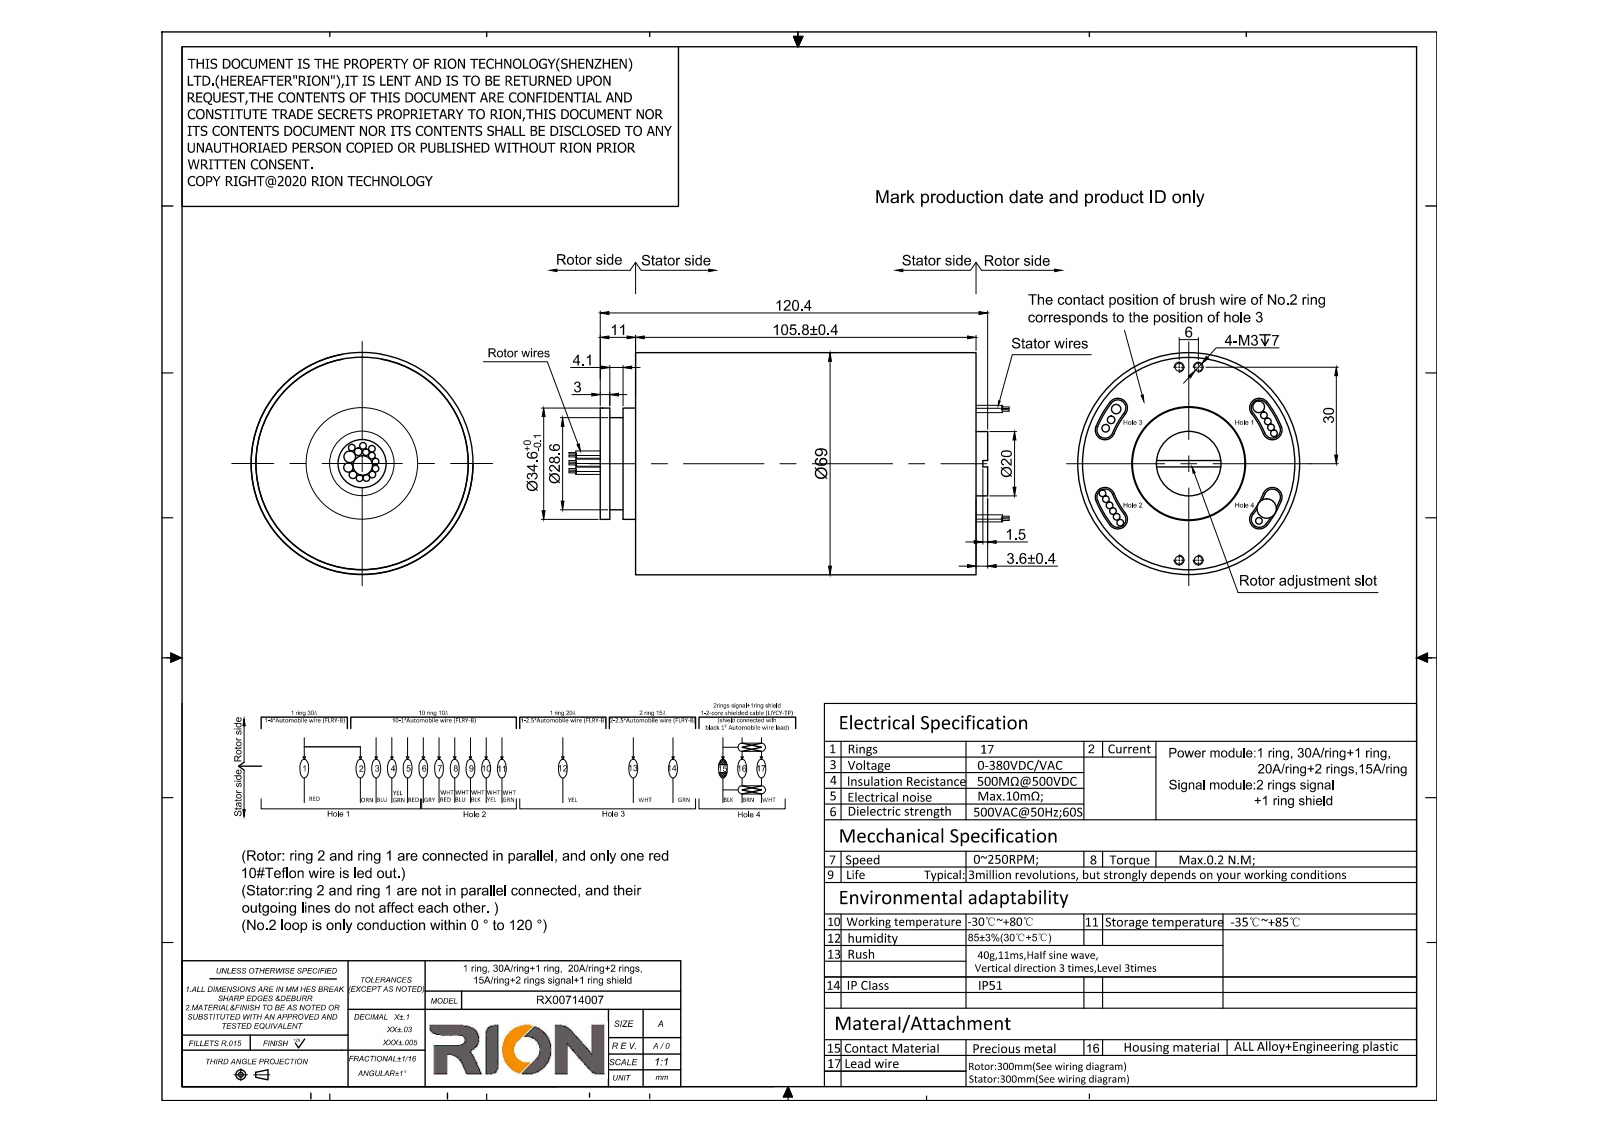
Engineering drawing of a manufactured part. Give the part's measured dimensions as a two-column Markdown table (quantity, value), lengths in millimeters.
| quantity | value |
| --- | --- |
| part name | RZ086-P0130-P0120-P0215-P1010-S03 |
| STEP written by | SolidWorks 2014 (CONFIG_CONTROL_DESIGN) |
| units | millimeters |
| bodies | 1 solid, 154 faces (45 planar, 101 cylindrical, 8 other) |
| overall size | 158.3 × 69 × 69 |
| volume | 408 982 mm³ |
| surface area | 37 604 mm² |
| round holes (diameter × count) | 2.5 × 4 |
| round bosses / shafts (diameter × count) | 2 × 23, 3.6 × 2, 2.9 × 2, 2.4 × 2, 69 × 1, 34.6 × 1, 28.6 × 1, 20 × 1 |
| partial cylindrical surfaces (radius × count) | 2.5 × 8, 25 × 1, 30 × 1 |
| main face-to-face distances | 105.8, 11, 116.8, 7.1, 3.9, 109.7, 3, 4.1, 8, 113.8 |
| hole center spacings | 6, 60, 60.3 |
